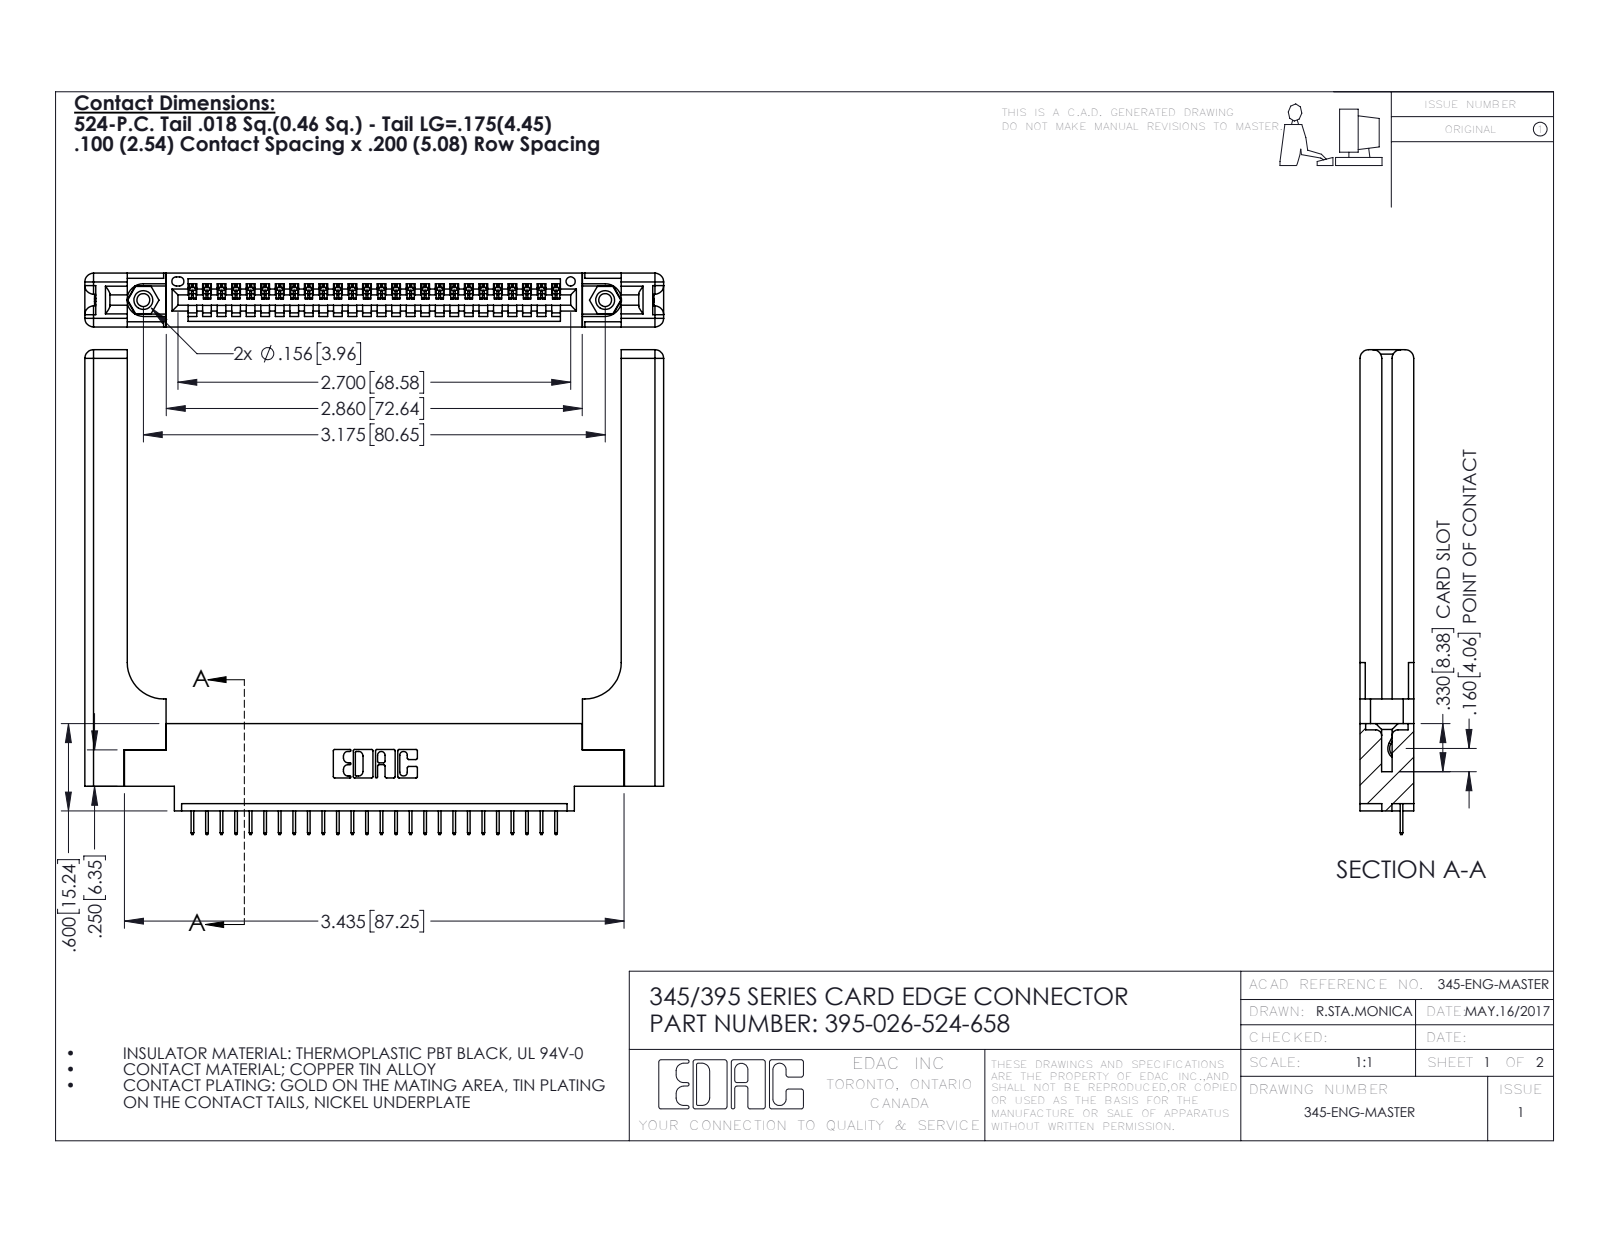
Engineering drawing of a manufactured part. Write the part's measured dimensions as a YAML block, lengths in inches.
part_name: "345-250-001_345-250-001-102; 345-292-001_345-293-124; 345-220-058_345-220-058; 345 Part_0.170 Offset - 0.156 Dia-TH (+1 more)"
step_written_by: "SolidWorks 2016 (CONFIG_CONTROL_DESIGN)"
units: inches
bodies: {solids: 31, faces: 1998, planar: 1428, cylindrical: 510, other: 60}
overall_size: [3.979, 3.332, 0.37]
volume: 1.084
surface_area: 26.63
round_holes:
  - {diameter: 0.089, count: 2}
  - {diameter: 0.125, count: 2}
  - {diameter: 0.156, count: 2}
  - {diameter: 0.064, count: 1}
round_bosses_or_shafts:
  - {diameter: 0.155, count: 2}
partial_cylinders:
  - {radius: 0.006, count: 52}
  - {radius: 0.01, count: 22}
  - {radius: 0.06, count: 16}
  - {radius: 0.007, count: 6}
  - {radius: 0.031, count: 6}
  - {radius: 0.026, count: 3}
  - {radius: 0.03, count: 2}
  - {radius: 0.031, count: 2}
face_to_face_distances: [0.37, 0.072, 0.298, 0.148, 0.15, 0.077, 0.22, 0.098, 0.272, 0.025]
hole_center_spacings: [0.27, 2.94, 3.175]
